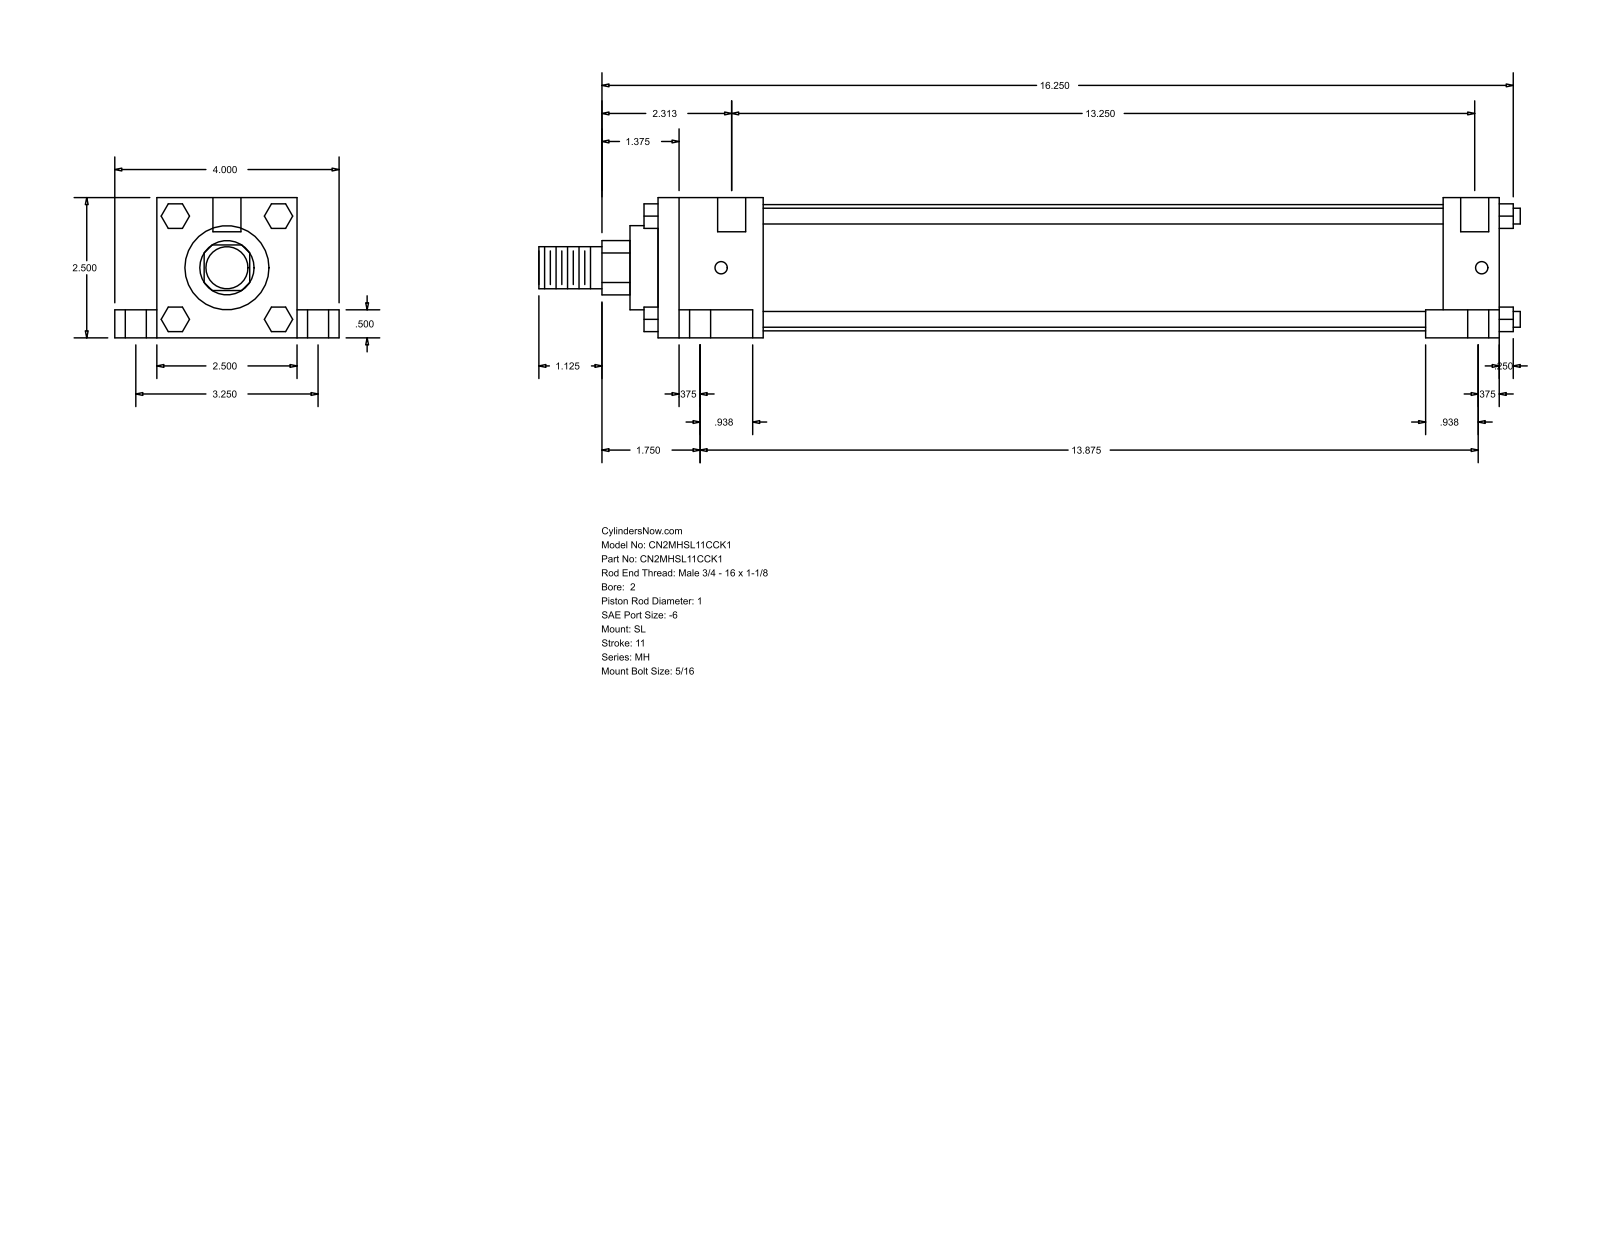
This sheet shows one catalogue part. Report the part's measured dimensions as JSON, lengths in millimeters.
{"part_name": "MH_SL__0200_1", "step_written_by": "GSSL Pune (CONFIG_CONTROL_DESIGN)", "units": "millimeters", "bodies": {"solids": 0, "faces": 148, "planar": 112, "cylindrical": 36, "other": 0}, "overall_size": [444.5, 101.6, 63.5], "round_holes": [[5.56, 4], [9.53, 4], [15.88, 4], [12.7, 2]], "round_bosses_or_shafts": [[7.14, 4], [57.15, 1], [38.1, 1], [25.4, 1], [19.05, 1]], "partial_cylinders_radius": [[12.29, 1]], "face_to_face_distances": [63.5, 381, 12.7, 19.05, 50.8, 82.55, 25.4, 355.6, 47.63, 307.97], "hole_center_spacings": [41.3, 42.36, 43.67, 82.54, 340.65, 344.48, 345.37, 352.43]}
